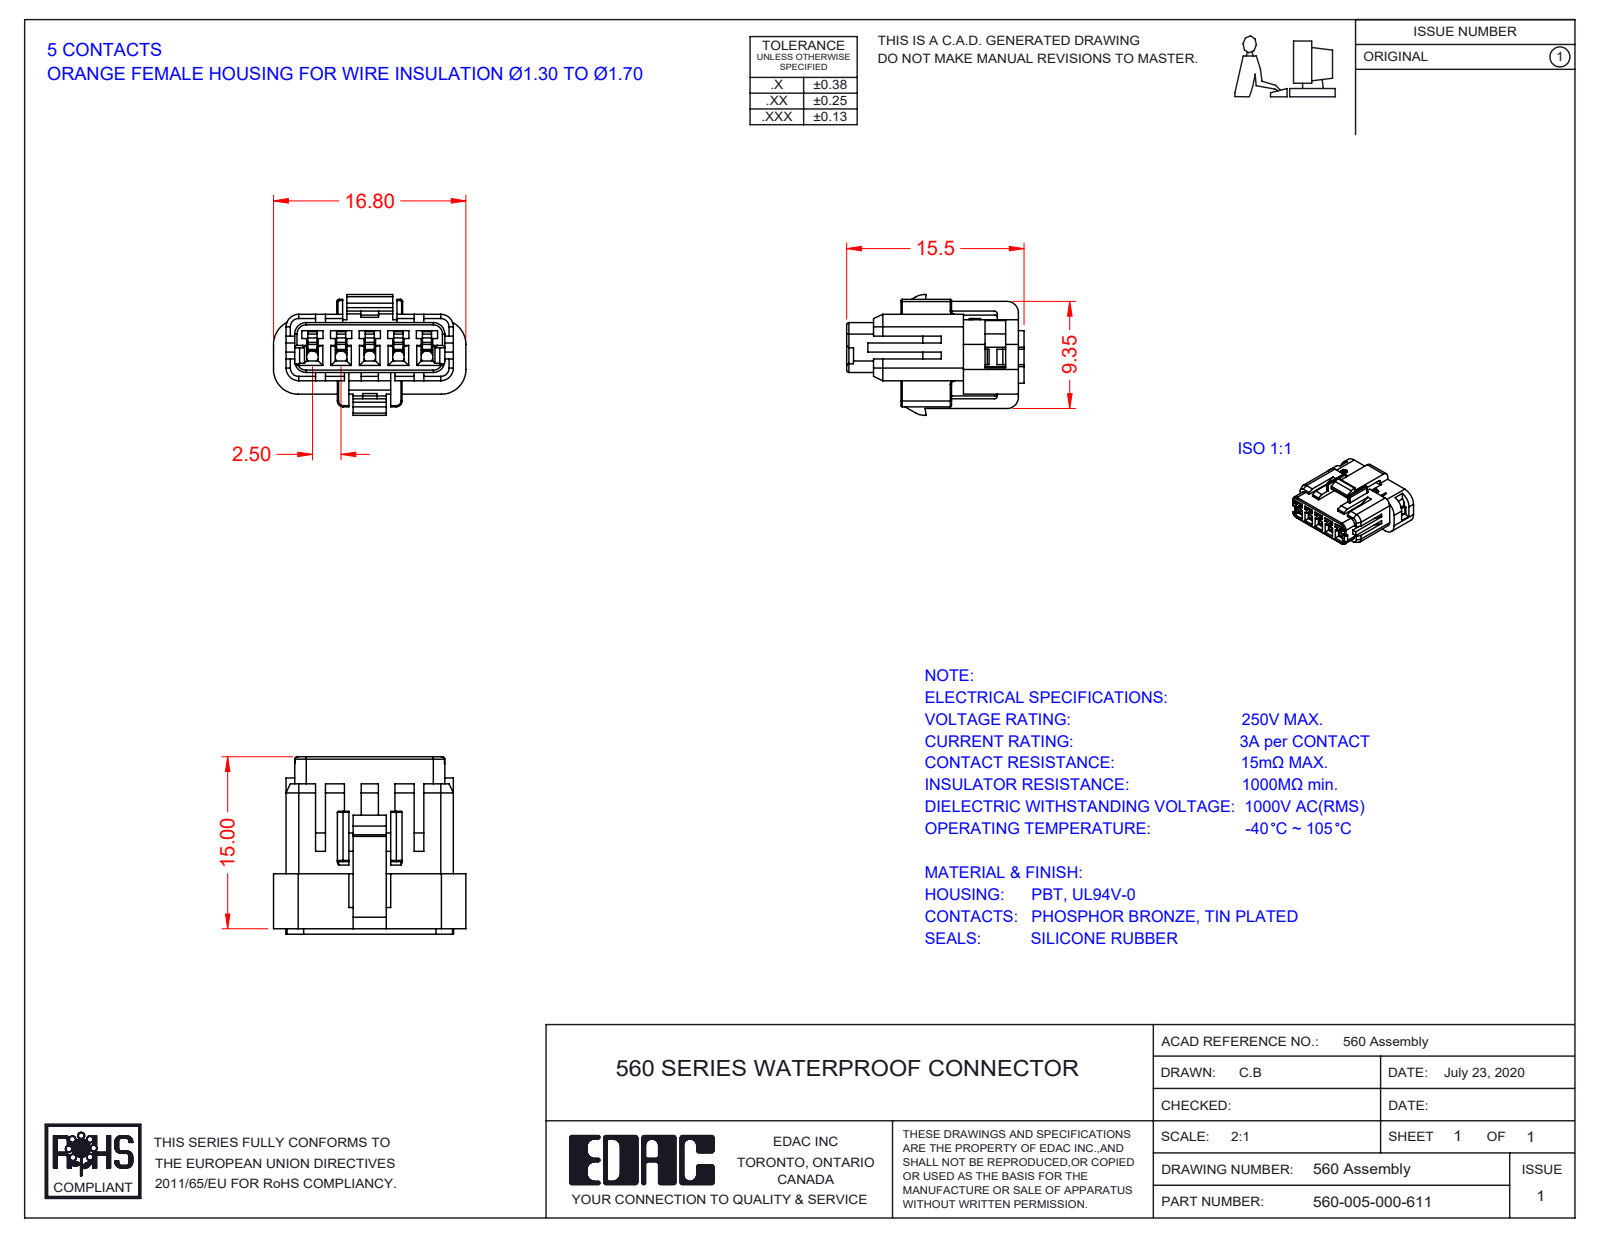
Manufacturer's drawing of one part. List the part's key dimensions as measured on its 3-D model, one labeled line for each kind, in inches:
Part name (STEP PRODUCT): 560-005-000-611; FEMALE_HOUSING_5POS_ORANGE; REAR-GASKET-5POS_ORANGE; REAR-INSULATOR-5POS-1
STEP written by: SolidWorks 2020 (CONFIG_CONTROL_DESIGN)
Units: inches
Bodies: 3 solids, 936 faces (560 planar, 172 cylindrical, 204 other)
Overall size (bounding box): 0.661 × 0.609 × 0.415
Volume: 0.063 in³ · Surface area: 3.861 in²
Round holes (diameter × count): ⌀0.059 ×5
Partial cylindrical surfaces — rounded edges, fillets, slot ends (radius × count): R0.004 ×13, R0.047 ×12, R0.008 ×10, R0.039 ×10, R0.006 ×8, R0.059 ×6, R0.012 ×4, R0.031 ×4
Main face-to-face distances: 0.15, 0.028, 0.222, 0.063, 0.031, 0.035, 0.122, 0.037, 0.154, 0.033
Hole centre spacings: 0.098, 0.197, 0.295, 0.394
